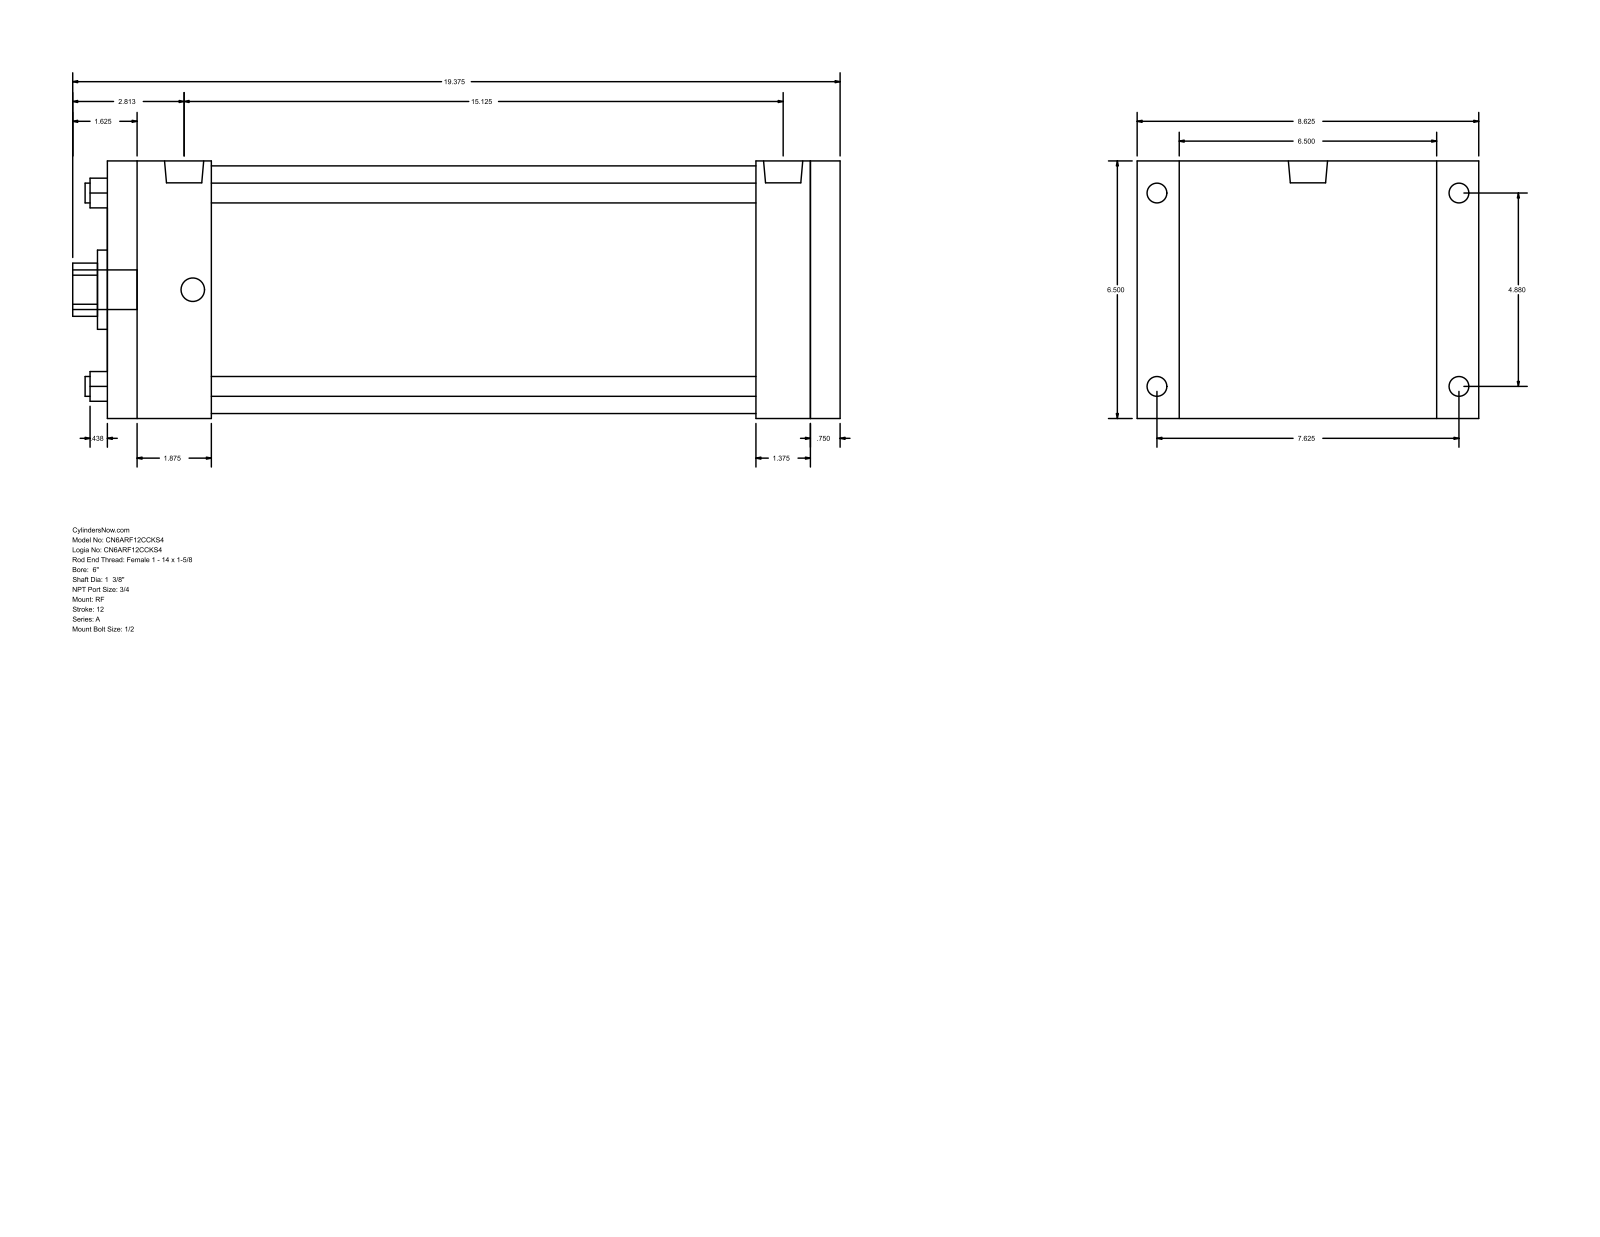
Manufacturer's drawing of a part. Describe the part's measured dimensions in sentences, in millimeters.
The part is named "A_RF__0600_1.375". Its 3-D file was written by "GSSL Pune (CONFIG_CONTROL_DESIGN)". It is 0 solids with 92 faces: 64 planar, 28 cylindrical and 0 other. Overall it measures 492.12 by 219.07 by 165.1 millimeters. Round holes: 4 of diameter 12.7, 1 of diameter 34.92, 1 of diameter 50.8, 1 of diameter 158.75. Round bosses or shafts: 4 of diameter 15.08, 4 of diameter 12.7, 2 of diameter 25.12, 1 of diameter 25.4. Partial cylindrical surfaces (rounded edges, fillets, slot ends): 1 of radius 17.06. The main face-to-face distances are 165.1, 469.89, 19.05, 450.84, 66.67, 384.17, 403.22, 415.92, 349.25, 34.92. The hole center spacings are 87.65, 123.96, 175.31.
